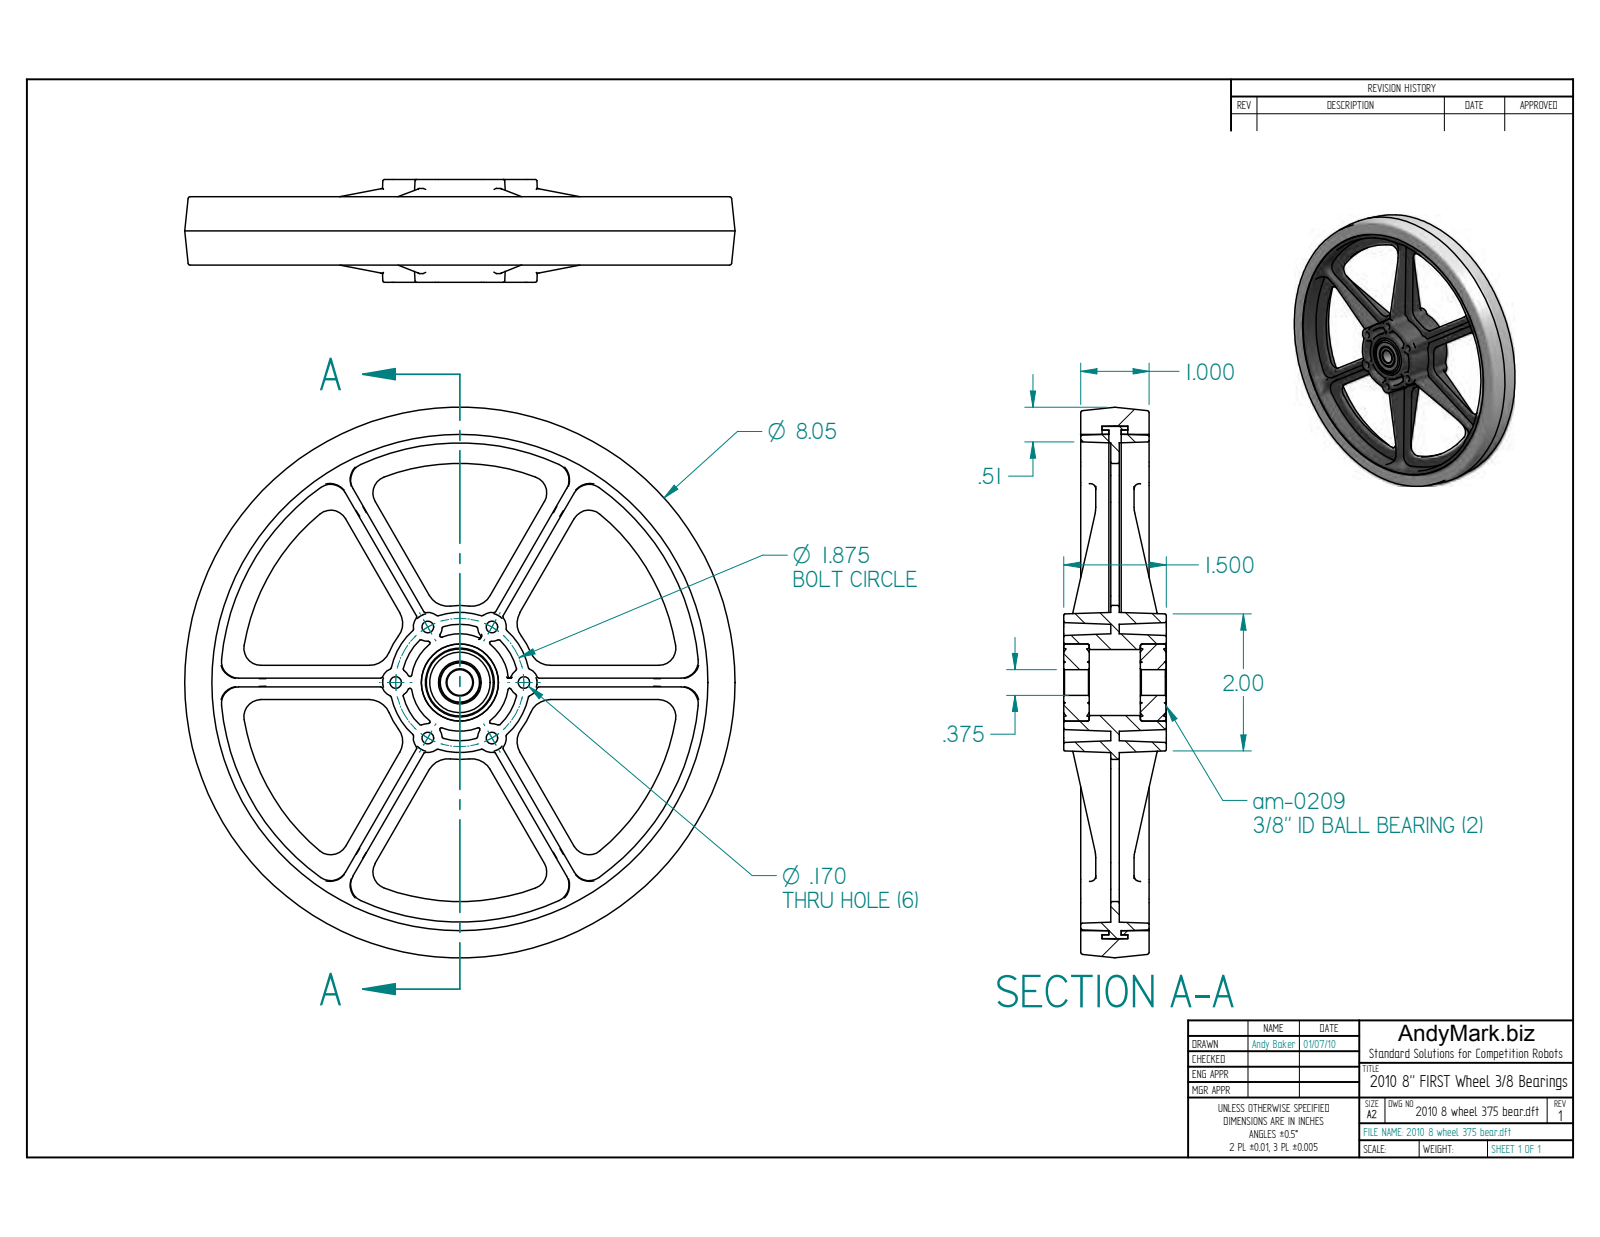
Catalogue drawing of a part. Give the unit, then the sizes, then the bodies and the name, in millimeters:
Units: millimetres
Overall size (bounding box): 204.35 × 204.35 × 44.45
Round holes (diameter × count): ⌀4.32 ×6, ⌀9.53 ×1, ⌀24.43 ×1, ⌀28.56 ×1, ⌀184.15 ×1, ⌀187.35 ×1, ⌀190.09 ×1
Round bosses / shafts (diameter × count): ⌀187.3 ×1, ⌀28.57 ×1
Partial cylindrical surfaces — rounded edges, fillets, slot ends (radius × count): R0.51 ×39, R6.35 ×12, R7.94 ×12, R28.57 ×1, R81.28 ×1
Main face-to-face distances: 12.7, 3.14, 11.13, 14.27, 25.4, 1.57, 7.94, 4.76, 17.46, 10.41
Hole centre spacings: 23.81, 41.24, 47.62, 23.82
Volume: 581 022 mm³ · Surface area: 294 731 mm²
Bodies: 7 solids, 1982 faces (242 planar, 254 cylindrical, 1486 other)
Part name (STEP PRODUCT): 2010 8 tread; 2010 8 hub; 1614Z Bearing
STEP written by: Unknown (CONFIG_CONTROL_DESIGN)
